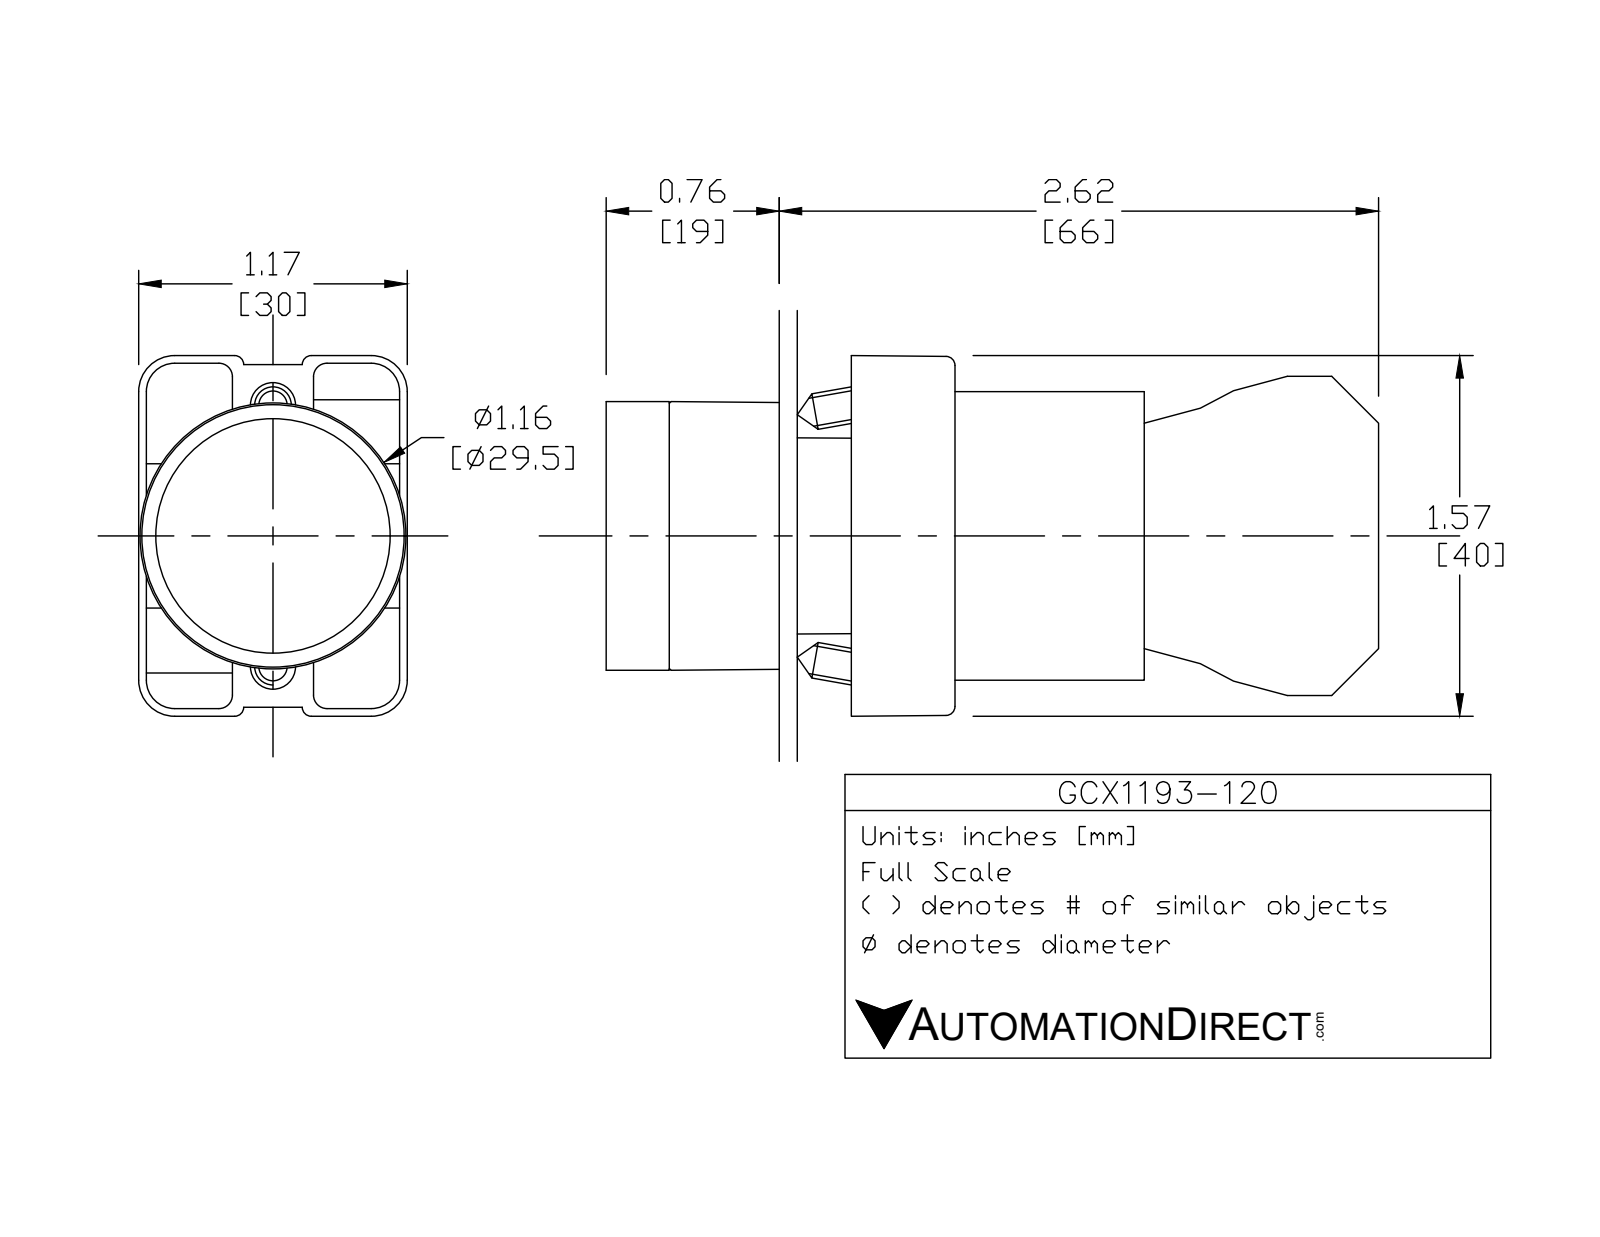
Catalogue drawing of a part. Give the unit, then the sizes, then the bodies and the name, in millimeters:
Units: millimetres
Overall size (bounding box): 84.3 × 40.2 × 29.9
Round holes (diameter × count): ⌀2 ×2, ⌀3.1 ×2, ⌀3.3 ×2, ⌀2.2 ×1, ⌀5 ×1, ⌀11.9 ×1, ⌀22.3 ×1, ⌀22.6 ×1, ⌀26 ×1
Round bosses / shafts (diameter × count): ⌀4 ×4, ⌀29.8 ×1, ⌀25.5 ×1, ⌀24 ×1, ⌀21.7 ×1, ⌀19.8 ×1, ⌀12.8 ×1
Partial cylindrical surfaces — rounded edges, fillets, slot ends (radius × count): R1.5 ×24, R1 ×12, R3.1 ×12, R4 ×12, R1 ×8, R3.3 ×2, R0.5 ×1, R1.6 ×1
Main face-to-face distances: 21, 51.3, 30.3, 14.7, 29.7, 0.8, 7, 0.8, 19, 14.6
Hole centre spacings: 6, 13.8, 12, 12.4
Volume: 45 790 mm³ · Surface area: 25 000 mm²
Bodies: 8 solids, 431 faces (252 planar, 148 cylindrical, 31 other)
Part name (STEP PRODUCT): ecx1040; ecx1029; GCX1193 OPERATOR; GCX1193-120 (+1 more)
STEP written by: SolidWorks 2016 (AUTOMOTIVE_DESIGN)
